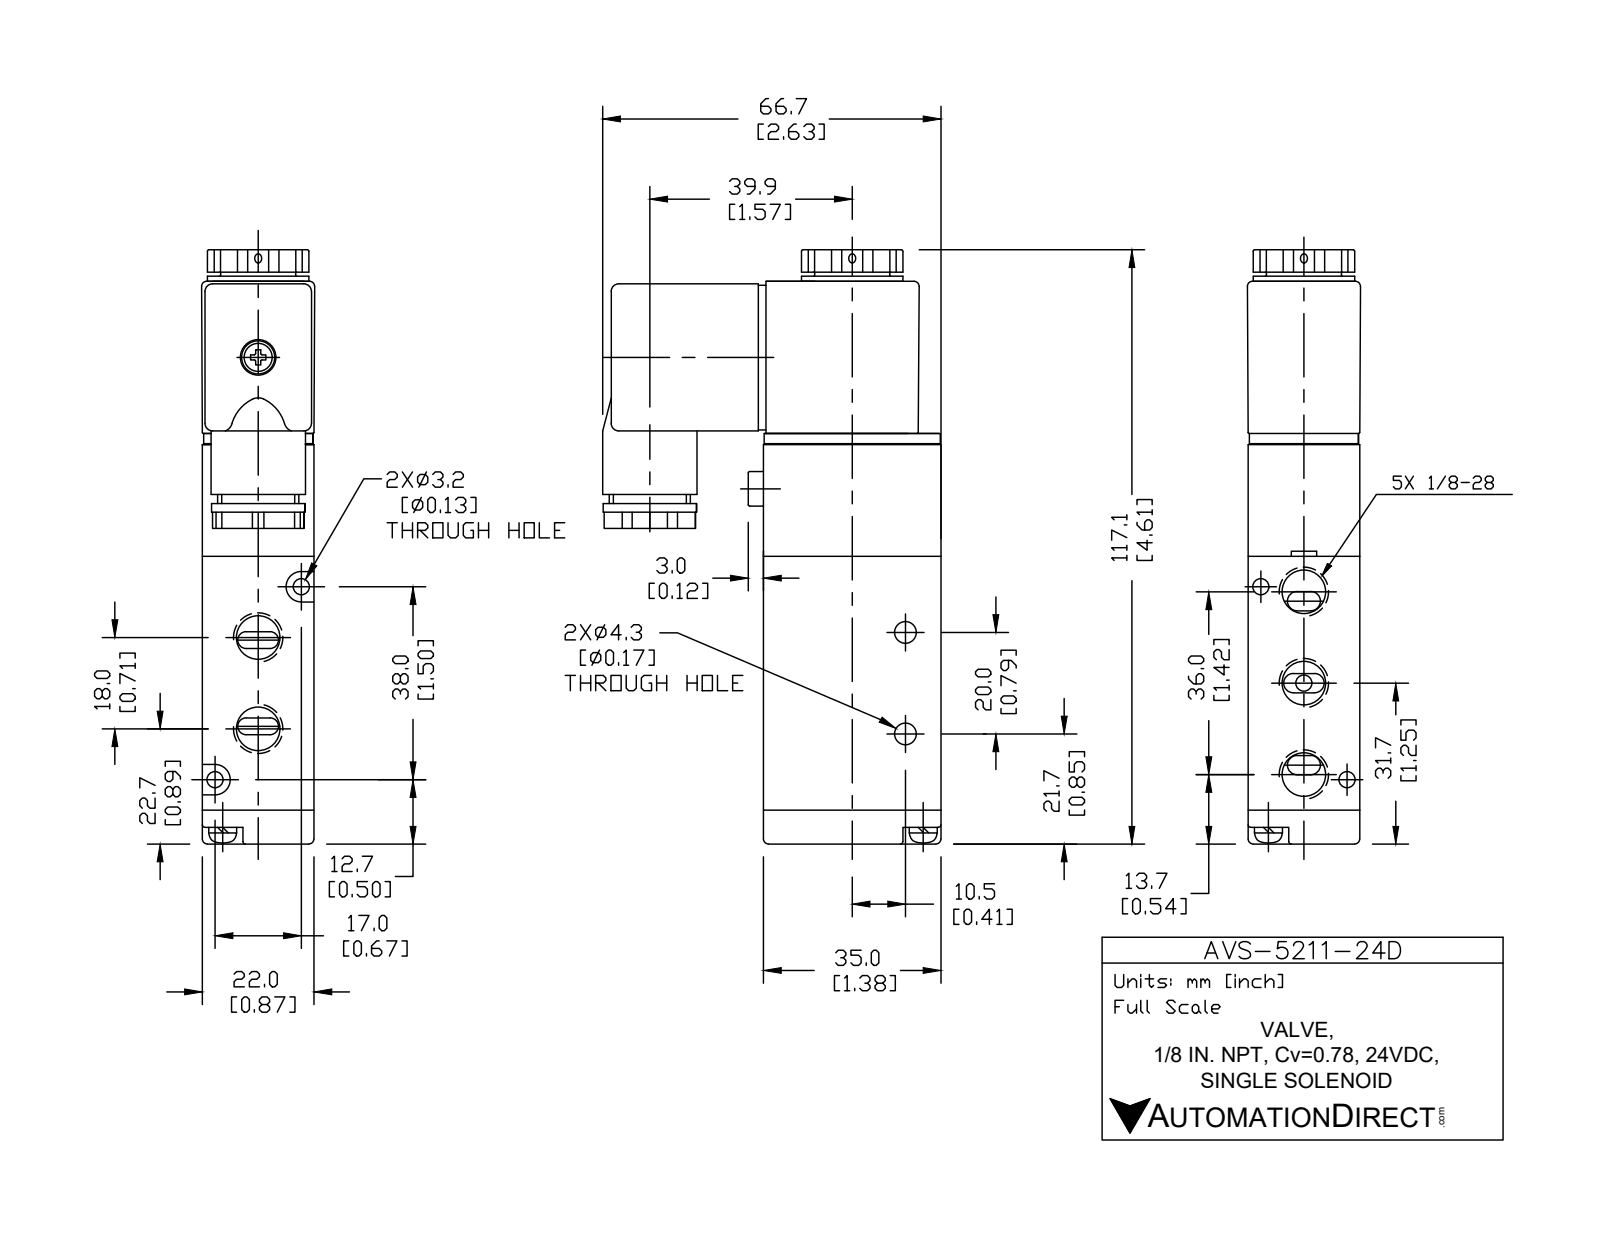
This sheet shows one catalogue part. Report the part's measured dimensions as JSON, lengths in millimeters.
{"part_name": "AVS-5211-24D", "step_written_by": "SolidWorks 2015 (CONFIG_CONTROL_DESIGN)", "units": "millimeters", "bodies": {"solids": 4, "faces": 195, "planar": 91, "cylindrical": 77, "other": 27}, "overall_size": [117.1, 66.7, 22], "volume_mm3": 101392, "surface_area_mm2": 24689, "round_holes": [[8.43, 5], [4.3, 2], [3.2, 1], [3.3, 1], [9.3, 1]], "round_bosses_or_shafts": [[20, 1], [18.6, 1], [18.4, 1], [16, 1], [14.8, 1], [6.7, 1]], "partial_cylinders_radius": [[1.5, 12], [1.54, 10], [0.5, 8], [1, 5], [3, 2]], "face_to_face_distances": [22, 0.5, 50, 21.5, 35, 6.7, 21, 110.4, 56.7, 30], "hole_center_spacings": [9, 18, 8.56, 13.12, 20.81, 27, 29.26, 37.96]}
